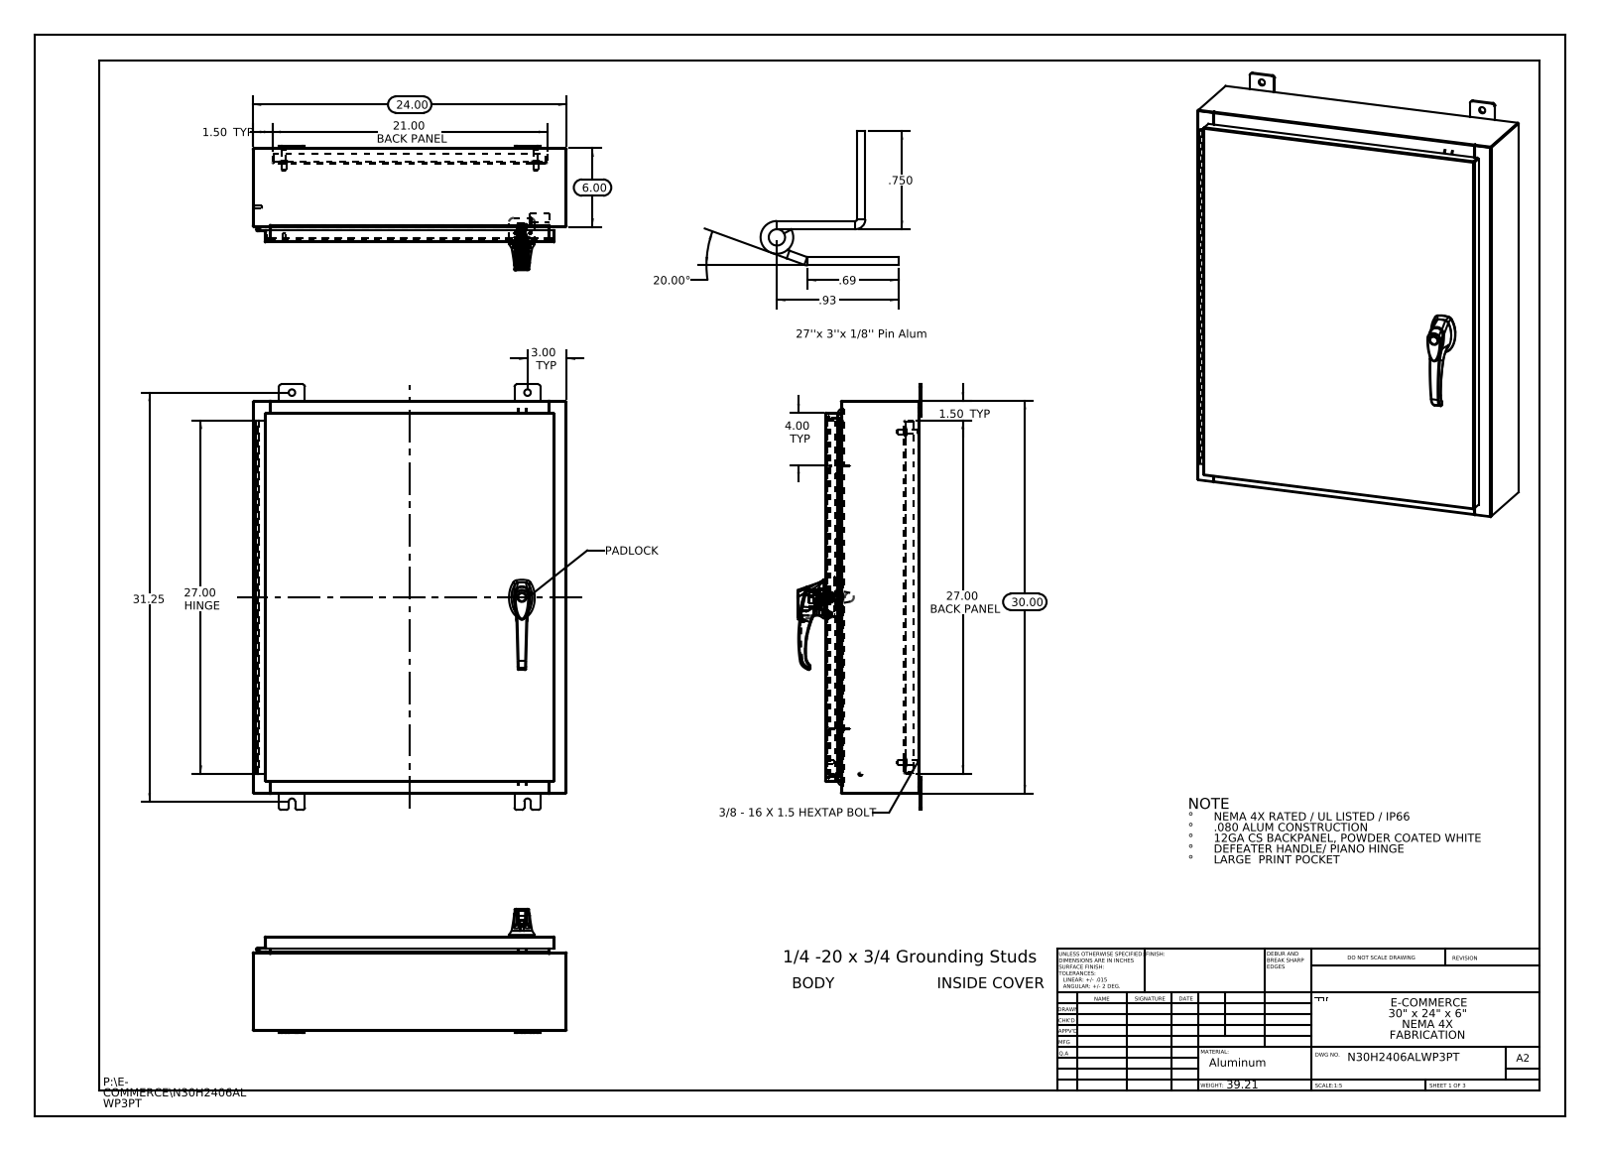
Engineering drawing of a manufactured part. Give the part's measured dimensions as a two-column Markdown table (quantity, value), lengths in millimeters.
| quantity | value |
| --- | --- |
| part name | N30H2406ALWP3PT 125 Pin Hinge; 297025; Quarter-20 CD Stud; 00005090 (+8 more) |
| STEP written by | SolidWorks 2013 (CONFIG_CONTROL_DESIGN) |
| units | millimeters |
| bodies | 37 solids, 2662 faces (971 planar, 993 cylindrical, 698 other) |
| overall size | 825.5 × 609.6 × 241.2 |
| volume | 4 197 000 mm³ |
| surface area | 4 054 000 mm² |
| round holes (diameter × count) | 12.7 × 8, 6.4 × 4, 3.5 × 3, 4.1 × 3, 2 × 2, 5.2 × 2, 8 × 2, 11.1 × 2, 3.2 × 1, 3.2 × 1, 5 × 1, 7 × 1 |
| round bosses / shafts (diameter × count) | 15.9 × 4, 9.5 × 4, 8.4 × 4, 4 × 4, 3.6 × 4, 8 × 3, 6 × 3, 30 × 1 |
| partial cylindrical surfaces (radius × count) | 3 × 37, 0.2 × 33, 0.3 × 24, 4.8 × 24, 2.2 × 18, 1 × 15, 0.7 × 12, 0.2 × 6 |
| main face-to-face distances | 1.9, 181, 2.6, 179.1, 182.9, 25.4, 27.3, 153.7, 155.6, 29.9 |
| hole center spacings | 212.6, 7.5, 15.9, 21.4, 31.8, 33.4, 39.6, 47.2 |
